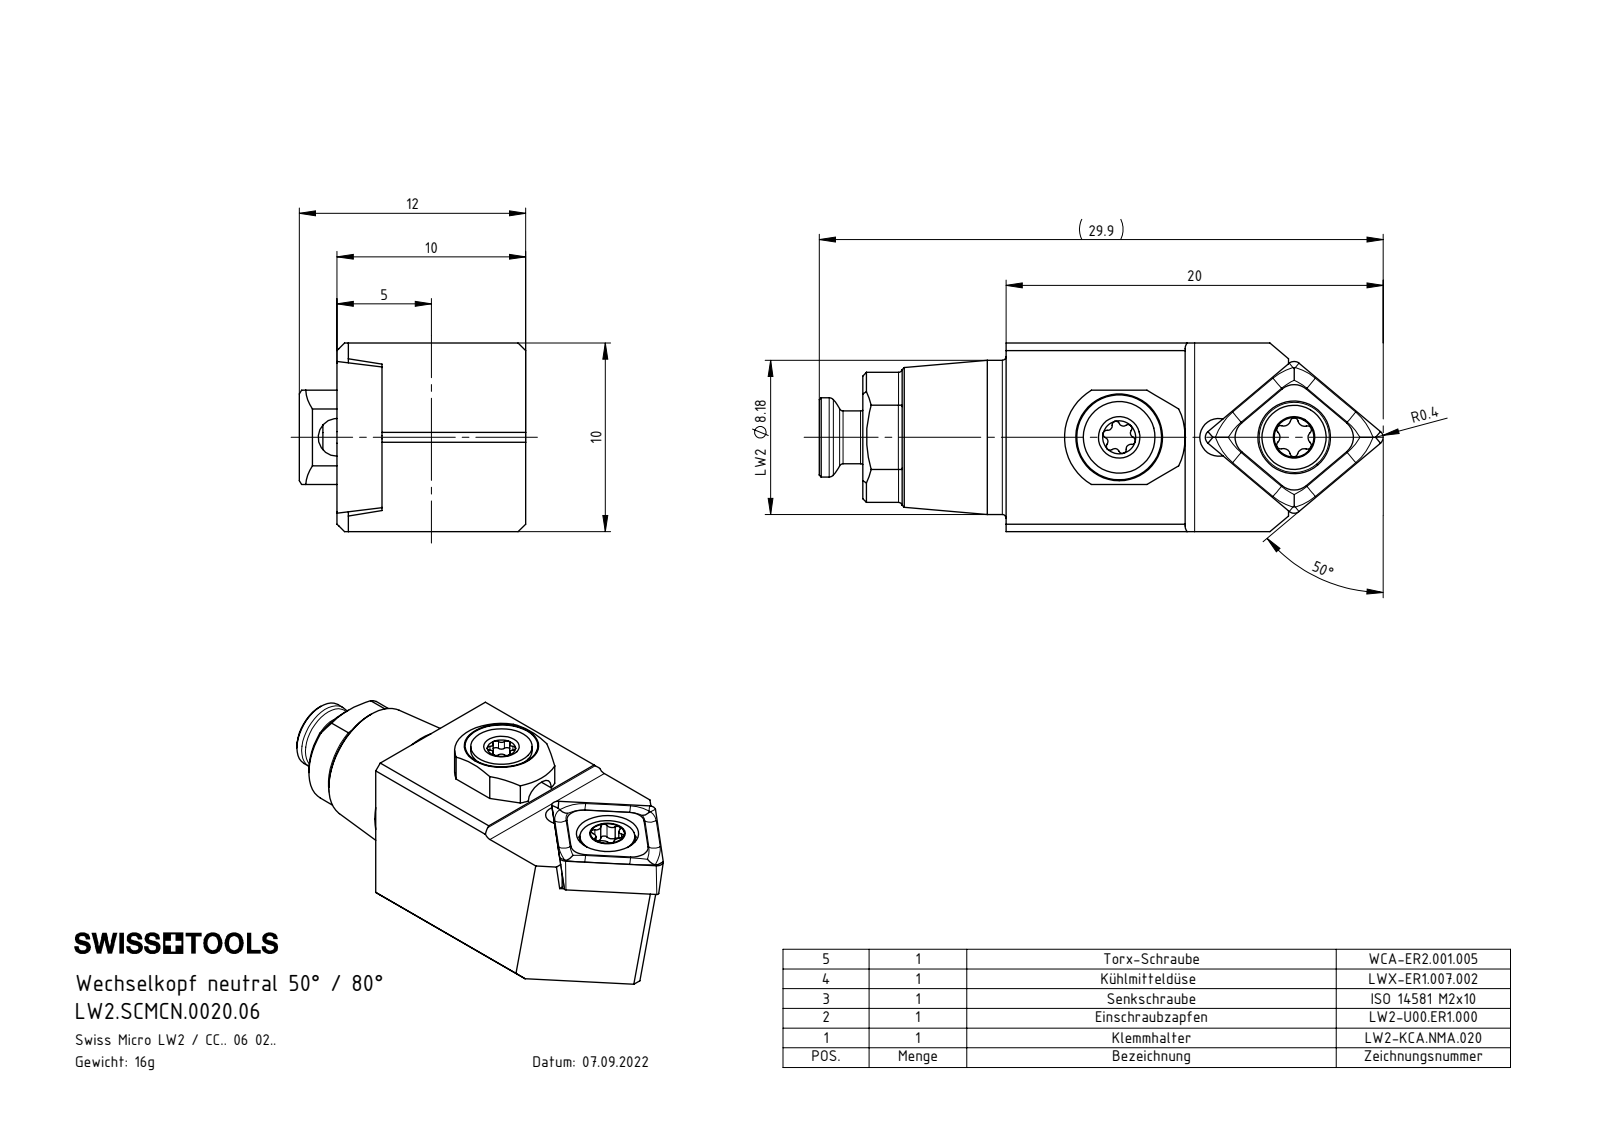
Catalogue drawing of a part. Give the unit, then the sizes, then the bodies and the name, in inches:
Units: inches
Overall size (bounding box): 1.177 × 0.472 × 0.394
Round holes (diameter × count): ⌀0.039 ×1, ⌀0.059 ×1, ⌀0.063 ×1, ⌀0.079 ×1, ⌀0.081 ×1, ⌀0.11 ×1, ⌀0.118 ×1, ⌀0.138 ×1, ⌀0.152 ×1
Round bosses / shafts (diameter × count): ⌀0.322 ×1, ⌀0.165 ×1, ⌀0.157 ×1, ⌀0.15 ×1, ⌀0.134 ×1, ⌀0.118 ×1, ⌀0.11 ×1, ⌀0.098 ×1
Partial cylindrical surfaces — rounded edges, fillets, slot ends (radius × count): R0.008 ×8, R0.007 ×6, R0.008 ×6, R0.009 ×6, R0.011 ×6, R0.014 ×5, R0.014 ×1, R0.02 ×1
Main face-to-face distances: 0.394, 0.3, 0.094, 0.37, 0.07, 0.024, 0.299, 0.043, 0.079, 0.315
Hole centre spacings: 0.157, 0.157, 0.208, 0.365, 0.365
Volume: 0.117 in³ · Surface area: 2.646 in²
Bodies: 6 solids, 187 faces (61 planar, 63 cylindrical, 63 other)
Part name (STEP PRODUCT): WCA-ER2.001.005_A; LWX-ER1.007.002; LW2-U00.ER1.000_A; LW2.SCMCN.0020.06 (+3 more)
STEP written by: SolidWorks 2017 (CONFIG_CONTROL_DESIGN)
